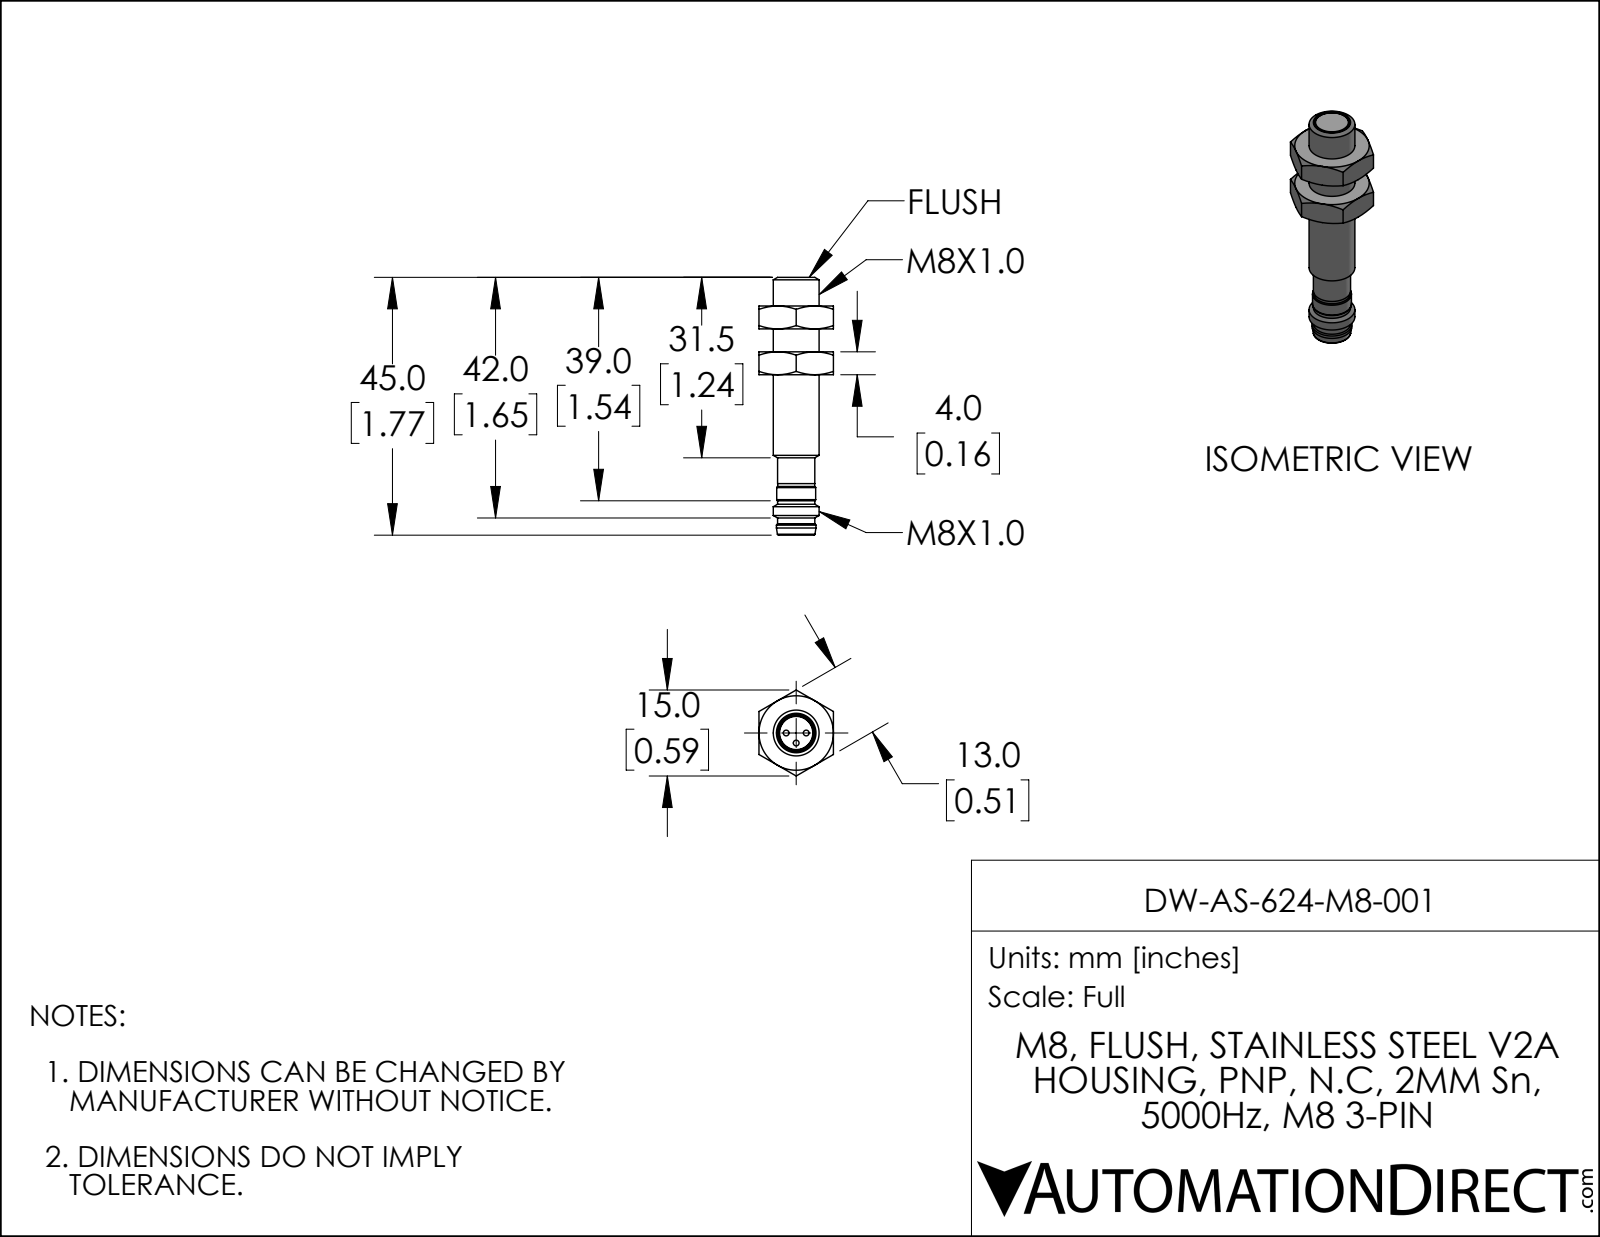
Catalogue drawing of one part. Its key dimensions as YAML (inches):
part_name: "DW-AS-624-M8-001"
step_written_by: "SolidWorks 2019 (AUTOMOTIVE_DESIGN)"
units: inches
bodies: {solids: 1, faces: 77, planar: 25, cylindrical: 14, other: 38}
overall_size: [1.772, 0.591, 0.512]
volume: 0.165
surface_area: 2.85
round_holes:
  - {diameter: 0.228, count: 1}
round_bosses_or_shafts:
  - {diameter: 0.039, count: 3}
  - {diameter: 0.315, count: 1}
  - {diameter: 0.272, count: 1}
  - {diameter: 0.268, count: 1}
  - {diameter: 0.256, count: 1}
  - {diameter: 0.254, count: 1}
face_to_face_distances: [0.157, 0.512, 0.315, 0.472, 0.197, 0.354, 0.669, 1.575, 1.22, 1.063]
